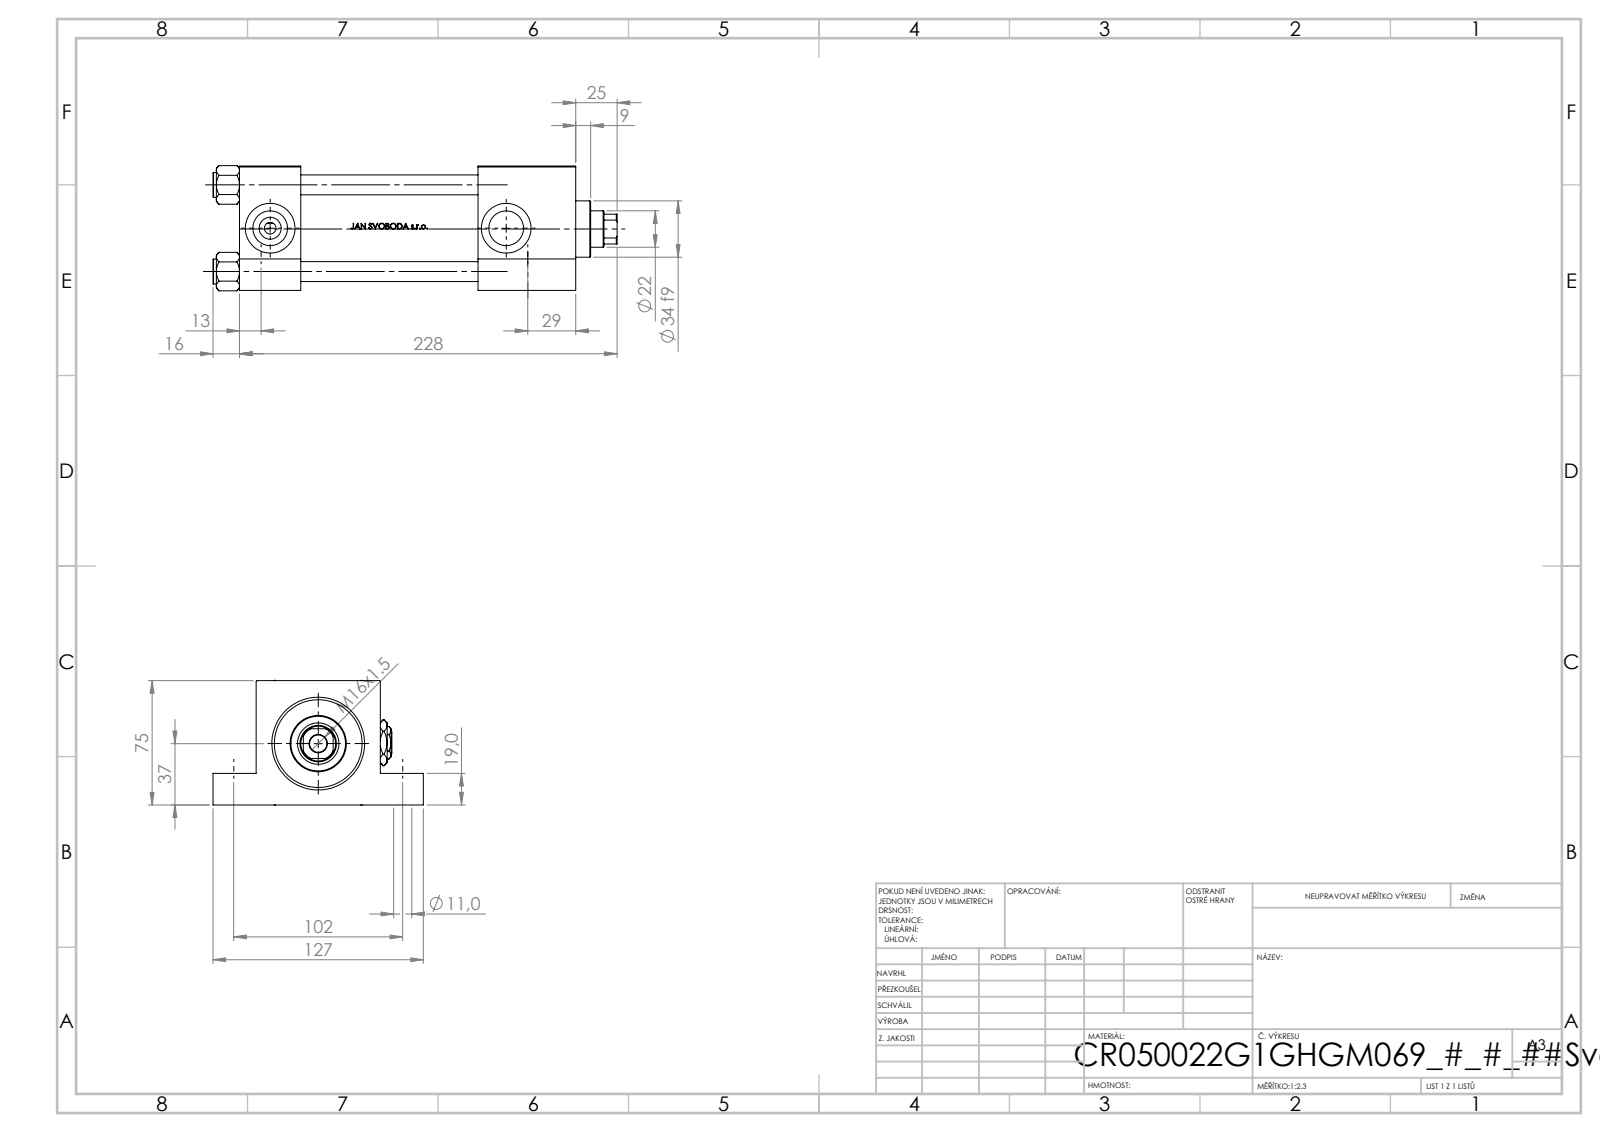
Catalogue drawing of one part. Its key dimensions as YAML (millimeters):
part_name: "V215CR_G_Body; V215CR_VCP_G; NUT_M5_G; Zatka_pro_OIL_PORT (+2 more)"
step_written_by: "SolidWorks 2019 (CONFIG_CONTROL_DESIGN)"
units: millimeters
bodies: {solids: 12, faces: 1134, planar: 454, cylindrical: 128, other: 552}
overall_size: [244, 127, 75.54]
volume: 817673
surface_area: 188397
round_holes:
  - {diameter: 11, count: 4}
  - {diameter: 12, count: 4}
  - {diameter: 7, count: 2}
  - {diameter: 20.96, count: 2}
  - {diameter: 30, count: 2}
  - {diameter: 10.5, count: 1}
  - {diameter: 22, count: 1}
  - {diameter: 25, count: 1}
  - {diameter: 41, count: 1}
  - {diameter: 50, count: 1}
  - {diameter: 53, count: 1}
round_bosses_or_shafts:
  - {diameter: 15, count: 4}
  - {diameter: 56, count: 1}
  - {diameter: 34, count: 1}
partial_cylinders:
  - {radius: 10.5, count: 1}
face_to_face_distances: [75, 37, 203, 166, 19, 56, 144, 107, 59, 26]
hole_center_spacings: [52.3, 36.63, 37.34, 73.96, 102, 161, 190.59, 142.5]
